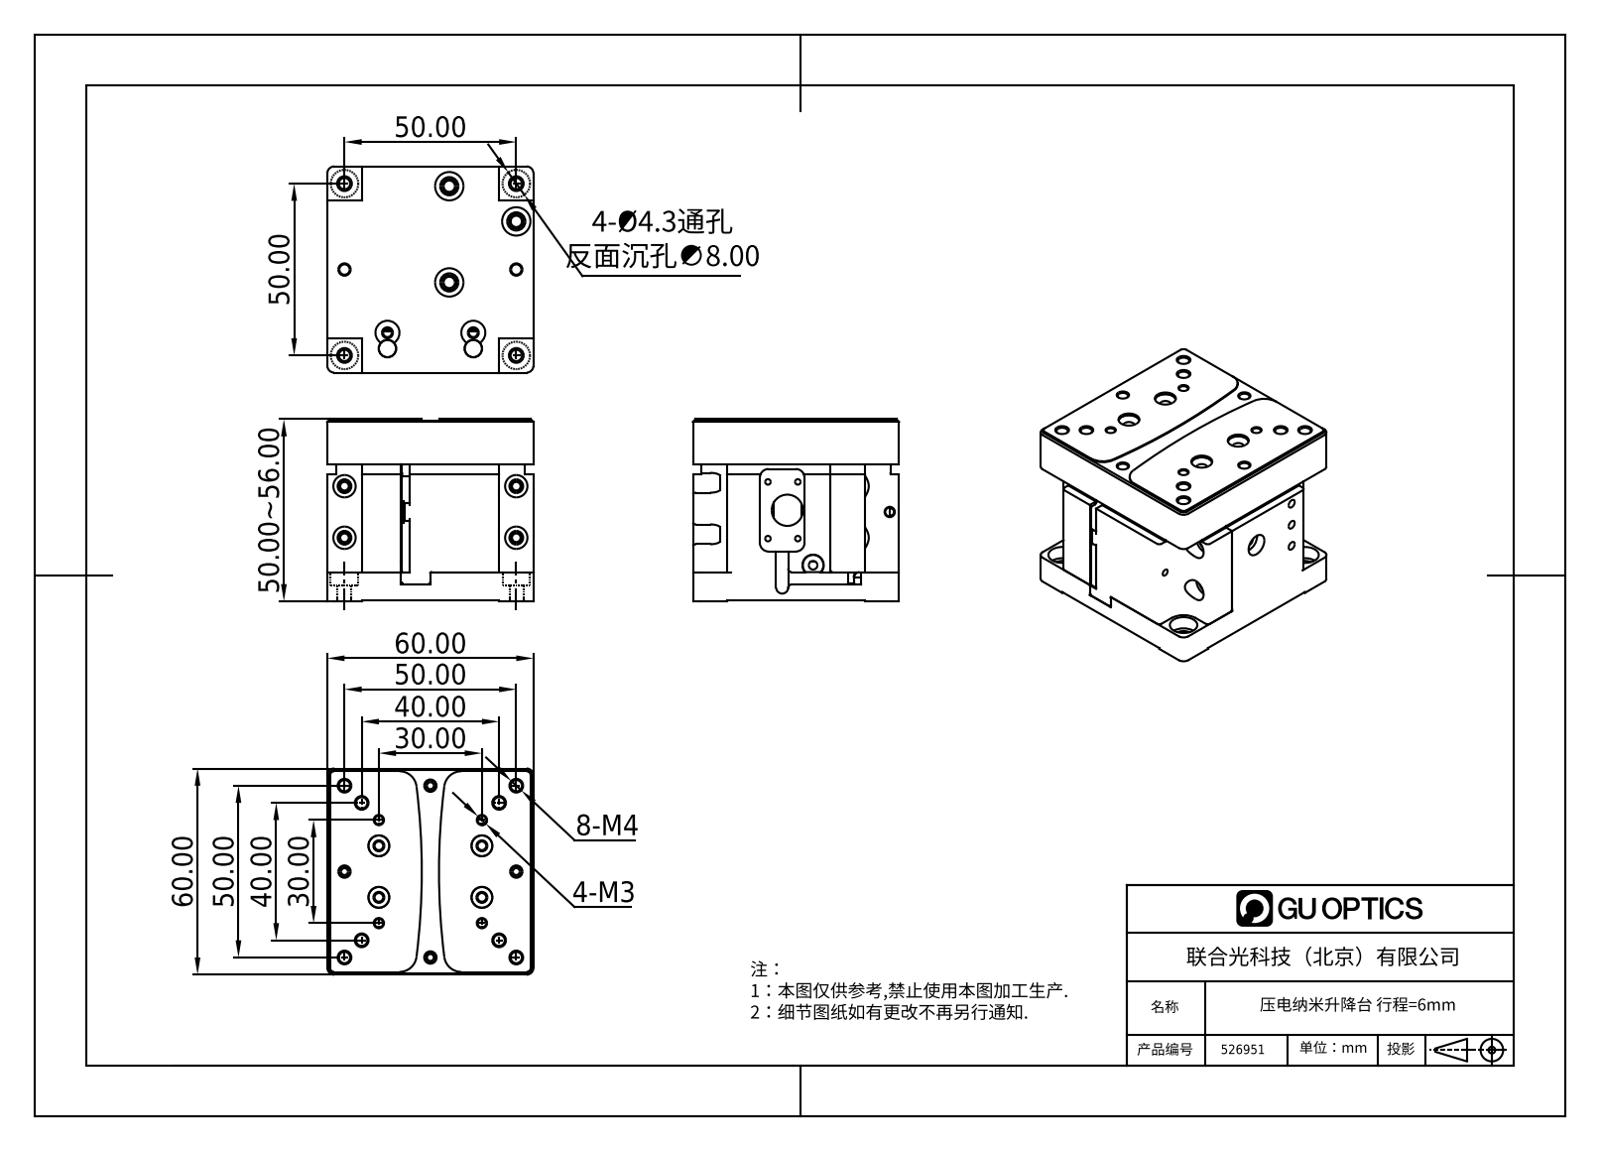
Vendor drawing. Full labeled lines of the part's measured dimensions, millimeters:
Part name (STEP PRODUCT): 526951
STEP written by: SolidWorks 2020 (CONFIG_CONTROL_DESIGN)
Units: millimetres
Bodies: 22 solids, 1105 faces (483 planar, 402 cylindrical, 220 other)
Overall size (bounding box): 60 × 60 × 53
Volume: 144 132 mm³ · Surface area: 62 705 mm²
Round holes (diameter × count): ⌀2.5 ×19, ⌀3.2 ×14, ⌀3.3 ×11, ⌀2.55 ×8, ⌀4.4 ×8, ⌀4.3 ×7, ⌀2 ×5, ⌀3 ×5, ⌀6.5 ×5, ⌀1.6 ×4, ⌀6.1 ×4, ⌀8 ×4
Round bosses / shafts (diameter × count): ⌀1.98 ×10, ⌀5.6 ×4
Partial cylindrical surfaces — rounded edges, fillets, slot ends (radius × count): R0.5 ×24, R1 ×17, R1.5 ×17, R2 ×17, R3 ×15, R5 ×12, R0.2 ×4, R1.2 ×4
Main face-to-face distances: 6.5, 0.5, 21, 27.5, 60, 3, 38, 35, 52.7, 12.5
Hole centre spacings: 35.36, 25, 30, 15, 7.07, 14.14, 18.03, 20.62
